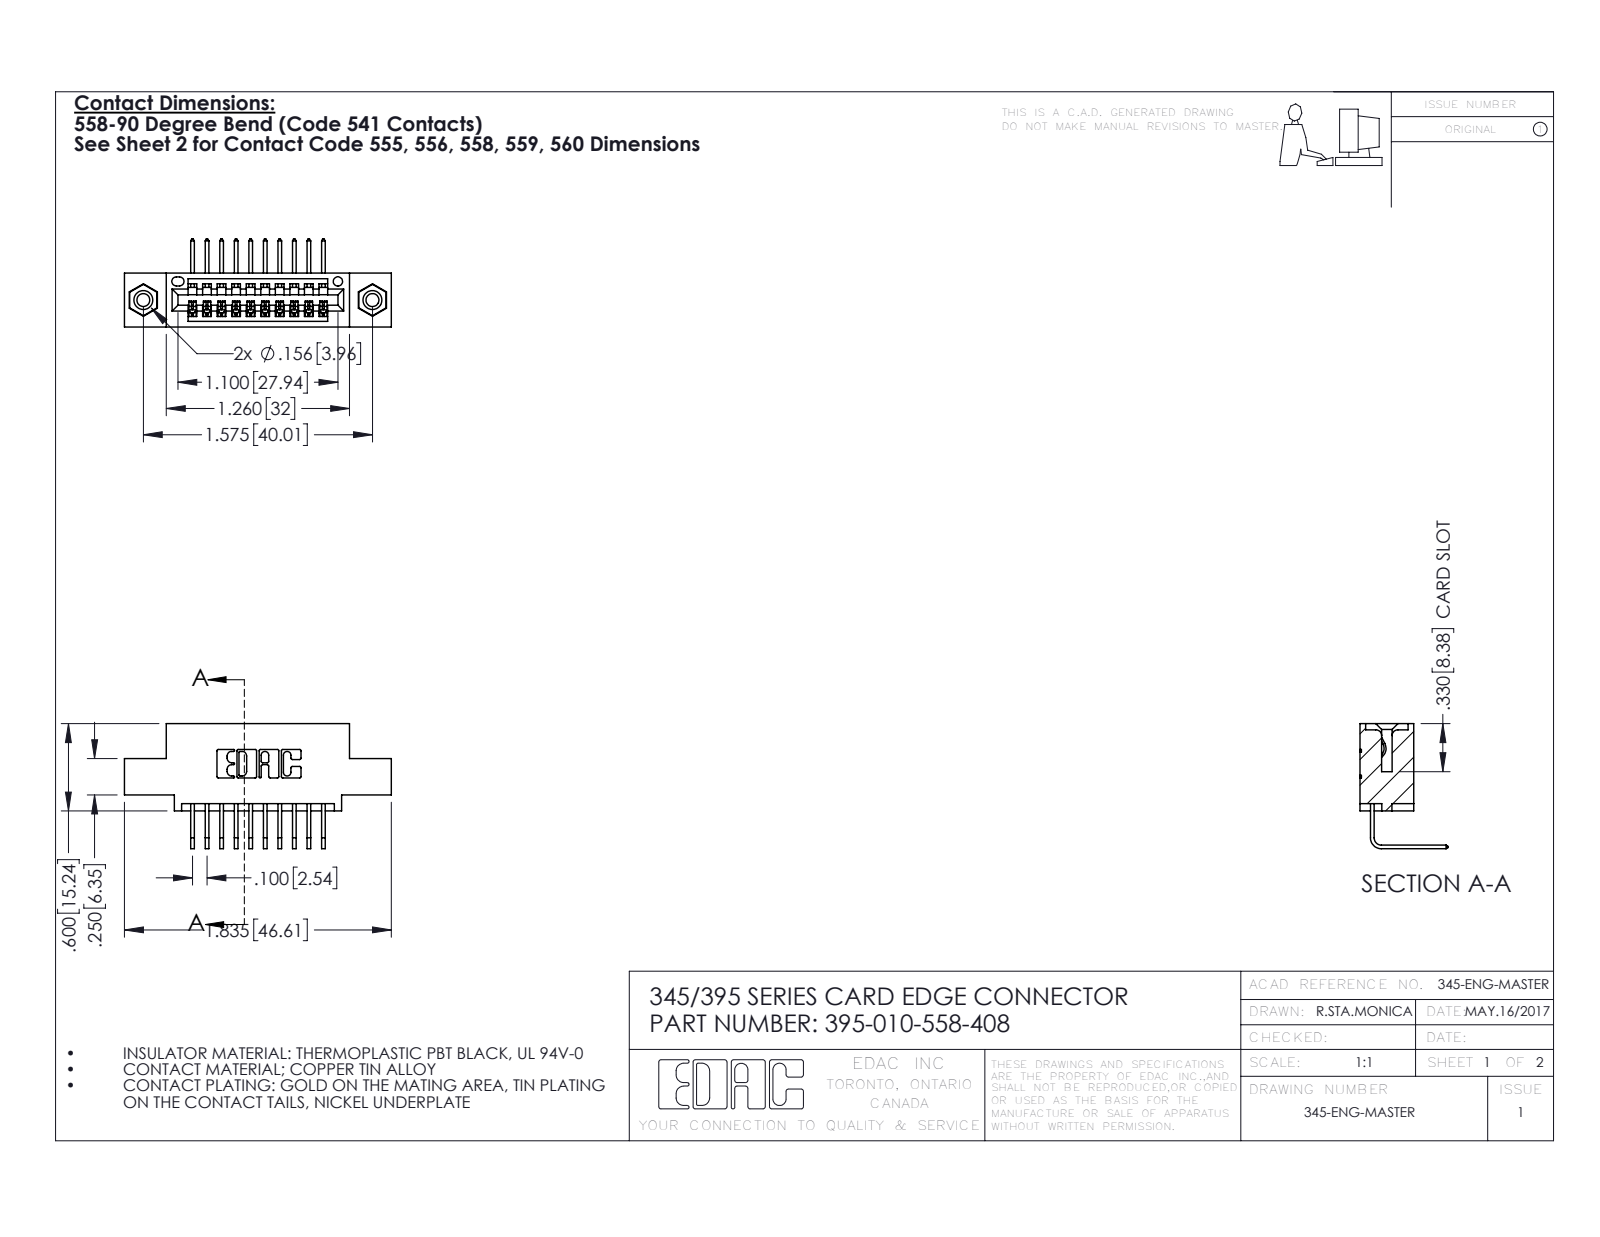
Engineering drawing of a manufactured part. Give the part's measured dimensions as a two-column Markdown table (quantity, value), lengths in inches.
| quantity | value |
| --- | --- |
| part name | 345 Part_0.110 Offset - 0.156 Dia-TI; 345-292-001_558 Tail - 2; 395-010-558-408; 345-250-001_345-250-003-102 |
| STEP written by | SolidWorks 2016 (CONFIG_CONTROL_DESIGN) |
| units | inches |
| bodies | 13 solids, 790 faces (536 planar, 238 cylindrical, 16 other) |
| overall size | 1.835 × 0.859 × 0.605 |
| volume | 0.251 in³ |
| surface area | 8.269 in² |
| round holes (diameter × count) | 0.089 × 2, 0.125 × 2, 0.156 × 2, 0.064 × 1 |
| round bosses / shafts (diameter × count) | 0.155 × 2 |
| partial cylindrical surfaces (radius × count) | 0.01 × 22, 0.006 × 20, 0.007 × 6, 0.031 × 6, 0.026 × 3, 0.031 × 2, 0.04 × 2, 0.014 × 1 |
| main face-to-face distances | 0.2, 0.072, 0.298, 0.37, 0.1, 0.098, 0.272, 0.025, 0.6, 0.06 |
| hole center spacings | 0.27, 1.344, 1.575 |
